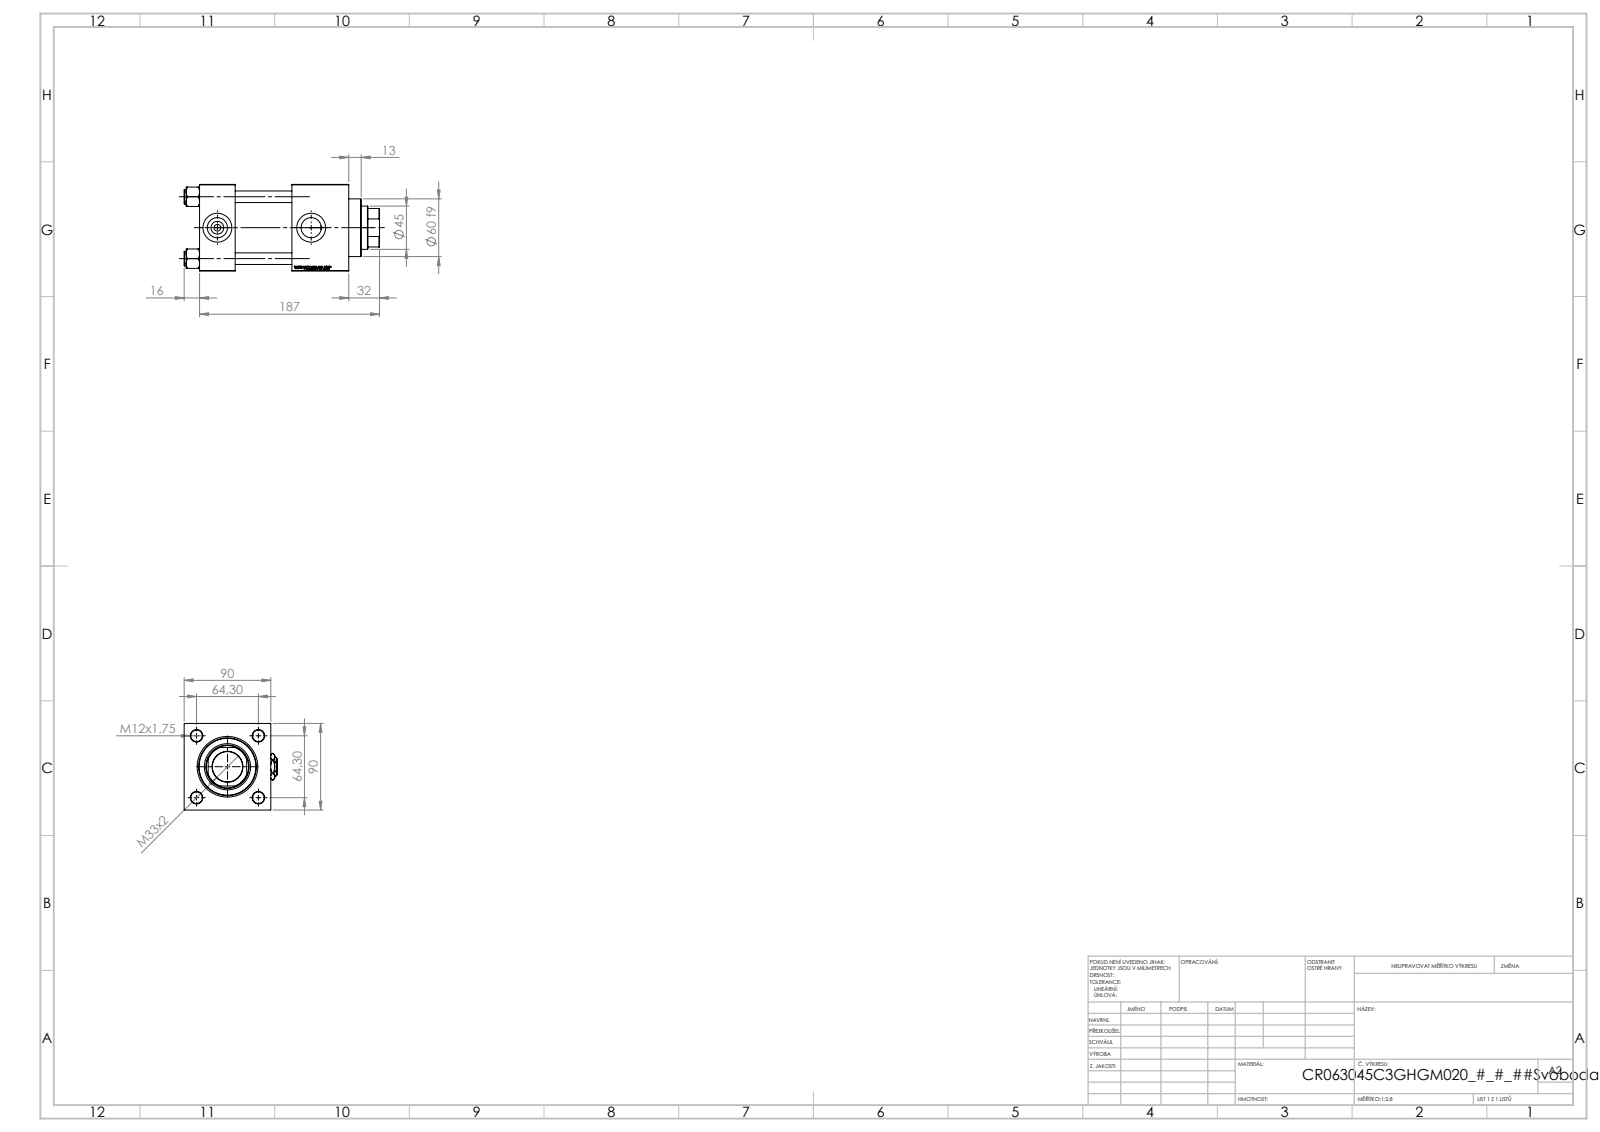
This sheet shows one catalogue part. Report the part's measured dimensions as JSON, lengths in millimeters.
{"part_name": "V215_VC_A; V215CR_VCP_C; NUT_M5_C; V215CR_C_Body (+2 more)", "step_written_by": "SolidWorks 2019 (CONFIG_CONTROL_DESIGN)", "units": "millimeters", "bodies": {"solids": 13, "faces": 1247, "planar": 573, "cylindrical": 96, "other": 578}, "overall_size": [203, 97, 90], "volume_mm3": 991563, "surface_area_mm2": 194717, "round_holes": [[12, 4], [7, 2], [20.96, 2], [30, 2], [31.5, 1], [45, 1], [48, 1], [50, 1], [60, 1], [63, 1]], "round_bosses_or_shafts": [[15, 4], [69, 1]], "partial_cylinders_radius": [[22, 1]], "face_to_face_distances": [90, 59, 37, 96, 118, 155, 89.8, 126.3, 89.3, 30.3], "hole_center_spacings": [45.47, 64.3, 90.93, 97.5]}
